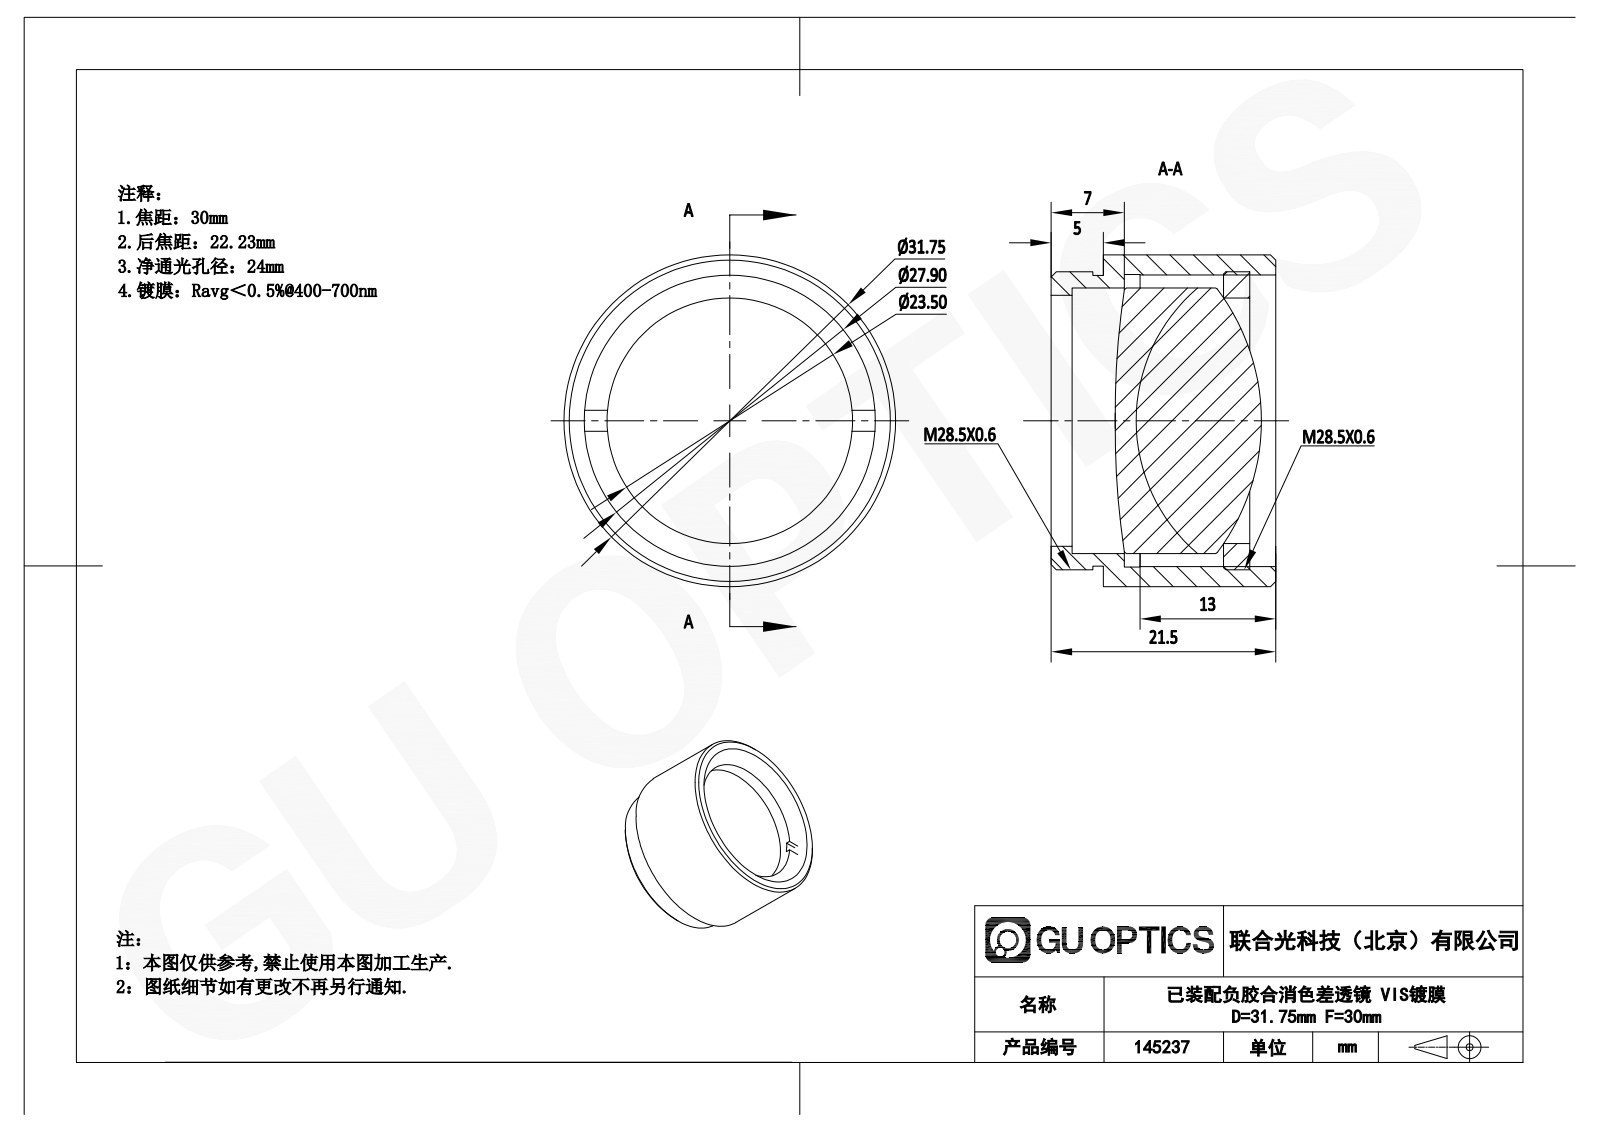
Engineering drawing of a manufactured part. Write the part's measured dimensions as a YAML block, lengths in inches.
part_name: "APD-ML25-030-VIS; GL31-025B-030-VIS_Solidworks; M28.5x0.6ѹȦ"
step_written_by: "SolidWorks 2022 (AUTOMOTIVE_DESIGN)"
units: inches
bodies: {solids: 4, faces: 56, planar: 16, cylindrical: 22, other: 18}
overall_size: [1.25, 1.25, 0.846]
volume: 0.624
surface_area: 13.04
round_holes:
  - {diameter: 0.925, count: 1}
  - {diameter: 0.945, count: 1}
  - {diameter: 1.098, count: 1}
  - {diameter: 1.102, count: 1}
round_bosses_or_shafts:
  - {diameter: 1.25, count: 1}
  - {diameter: 1.122, count: 1}
  - {diameter: 1.094, count: 1}
  - {diameter: 1, count: 1}
face_to_face_distances: [0.079, 0.197, 0.098, 0.453, 0.552, 0.65, 0.748, 0.846, 0.65, 0.196]
